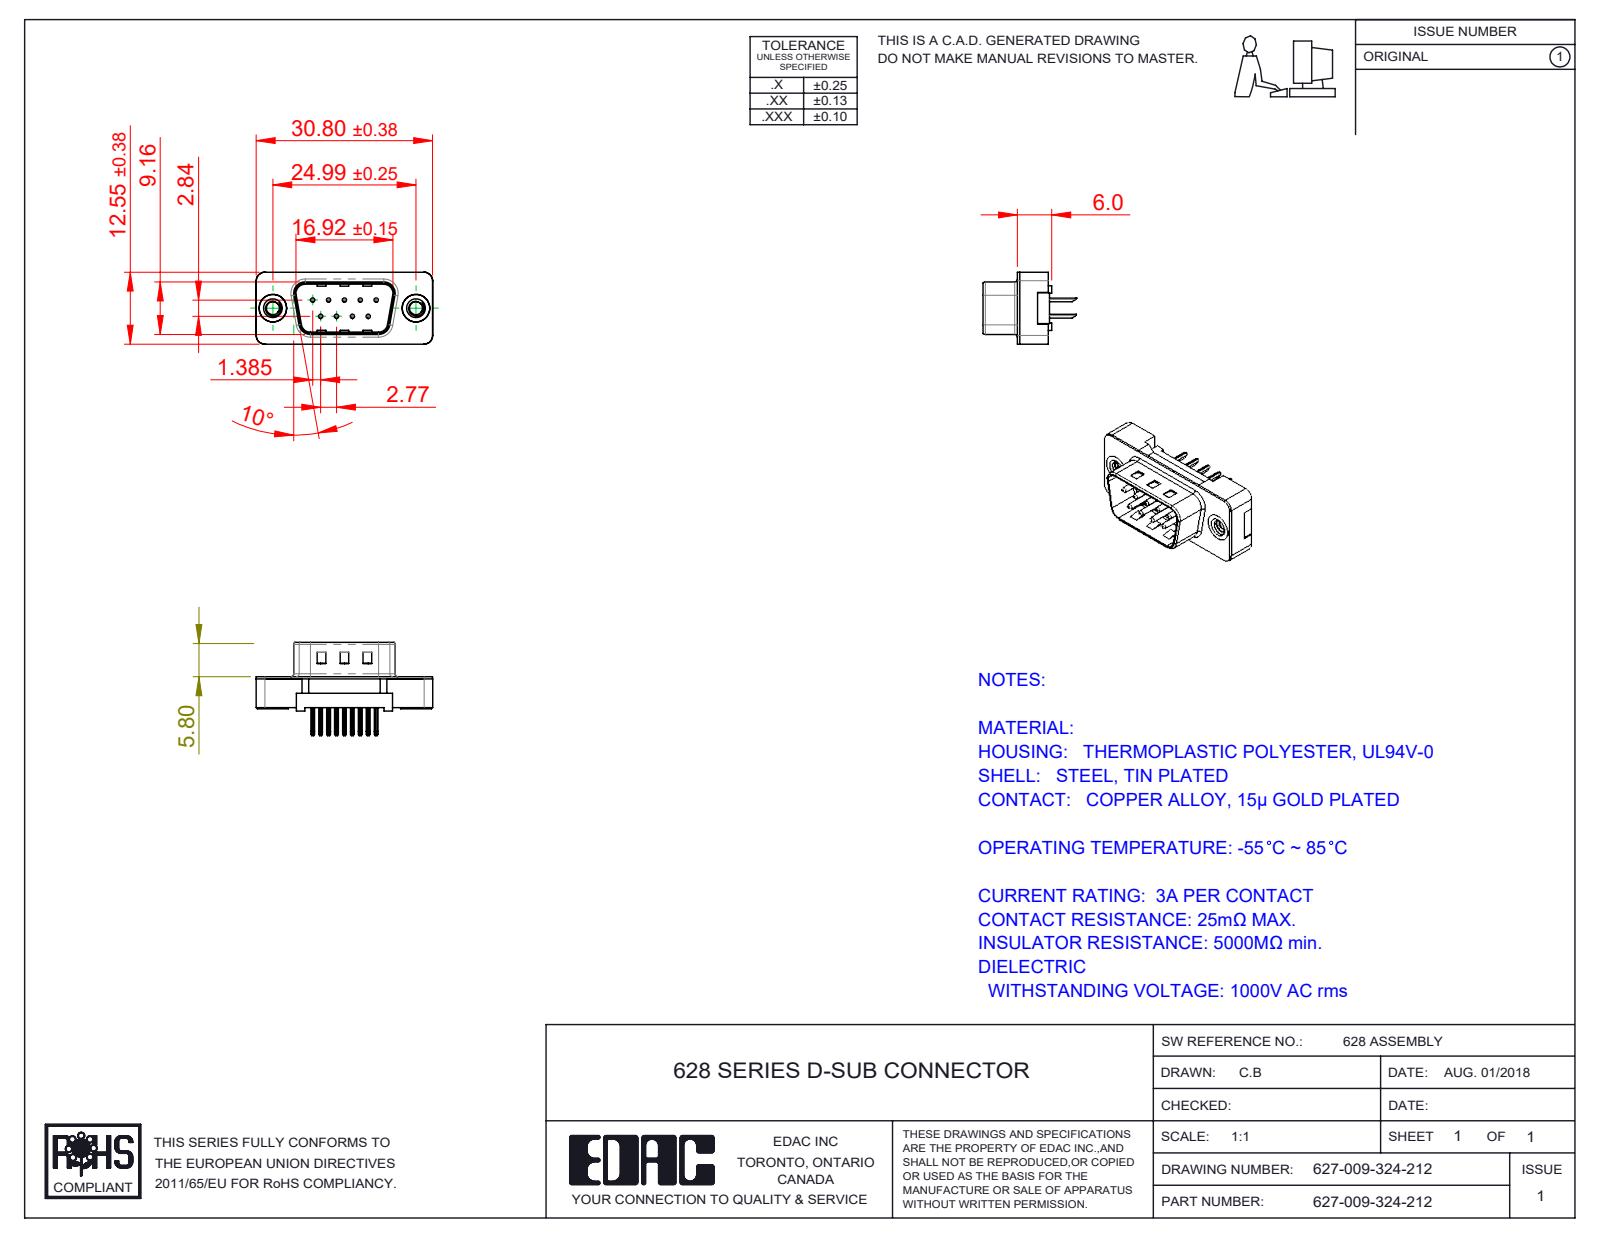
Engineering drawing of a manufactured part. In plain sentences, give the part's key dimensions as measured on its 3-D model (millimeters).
The part is named "627-009-324-212; 627 PB Contact Row 1_24; 627 PB 4-40 Threaded Rivet; 627 Plastic Body Housing_09 Contacts (+2 more)". Its 3-D file was written by "SolidWorks 2020 (CONFIG_CONTROL_DESIGN)". It is 13 solids with 783 faces: 481 planar, 240 cylindrical and 62 other. Overall it measures 30.81 by 16.3 by 12.55 millimeters. Its volume is 1 651 cubic millimeters and its surface area 3 404 square millimeters. Round holes: 9 of diameter 0.35, 9 of diameter 0.85, 2 of diameter 2.26, 2 of diameter 4, 2 of diameter 4.8, 2 of diameter 5. Round bosses or shafts: 9 of diameter 0.75, 2 of diameter 4.9. Partial cylindrical surfaces (rounded edges, fillets, slot ends): 18 of radius 0.25, 9 of radius 0.12, 8 of radius 0.5, 7 of radius 1.5, 4 of radius 0.9, 4 of radius 1.6, 4 of radius 2, 2 of radius 0.4. The main face-to-face distances are 0.4, 2.5, 5.4, 5, 2.9, 8.76, 2.1, 8.08, 0.68, 8.48. The hole center spacings are 3.16, 2.77, 5.04, 5.54, 7.49, 5.03, 7.09, 8.31.
